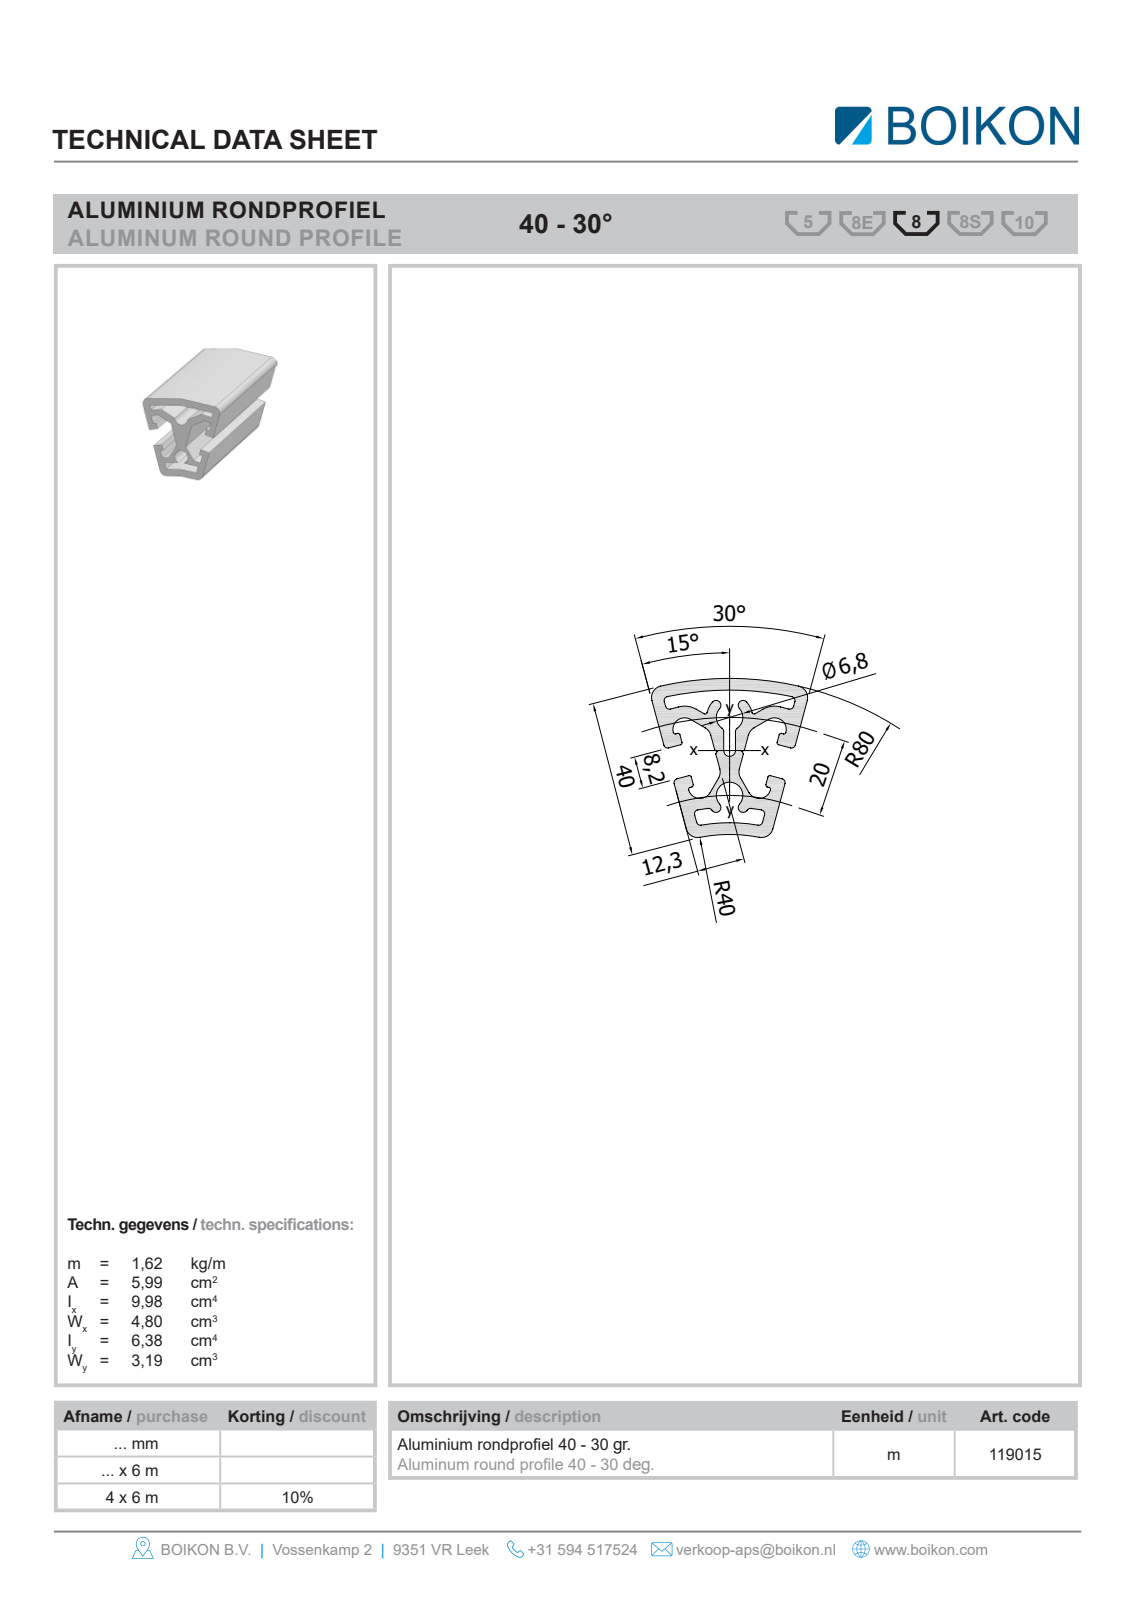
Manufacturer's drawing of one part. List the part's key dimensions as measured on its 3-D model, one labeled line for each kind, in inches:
Part name (STEP PRODUCT): Root; 119015Rondprofiel 40-30gr.BOIKON0
STEP written by: HiCAD 2013 1802.4 Build 509 (AUTOMOTIVE_DESIGN)
Units: inches
Bodies: 1 solid, 52 faces (38 planar, 14 cylindrical, 0 other)
Overall size (bounding box): 39.37 × 1.744 × 1.53
Volume: 38.06 in³ · Surface area: 577.7 in²
Round holes (diameter × count): ⌀0.268 ×1
Partial cylindrical surfaces — rounded edges, fillets, slot ends (radius × count): R0.118 ×4, R0.134 ×1, R1.575 ×1, R1.713 ×1, R1.85 ×1, R2.913 ×1, R3.012 ×1, R3.15 ×1
Main face-to-face distances: 0.138, 0.476, 0.114, 0.362, 0.272, 0.594, 0.024, 0.339, 0.177, 0.063
